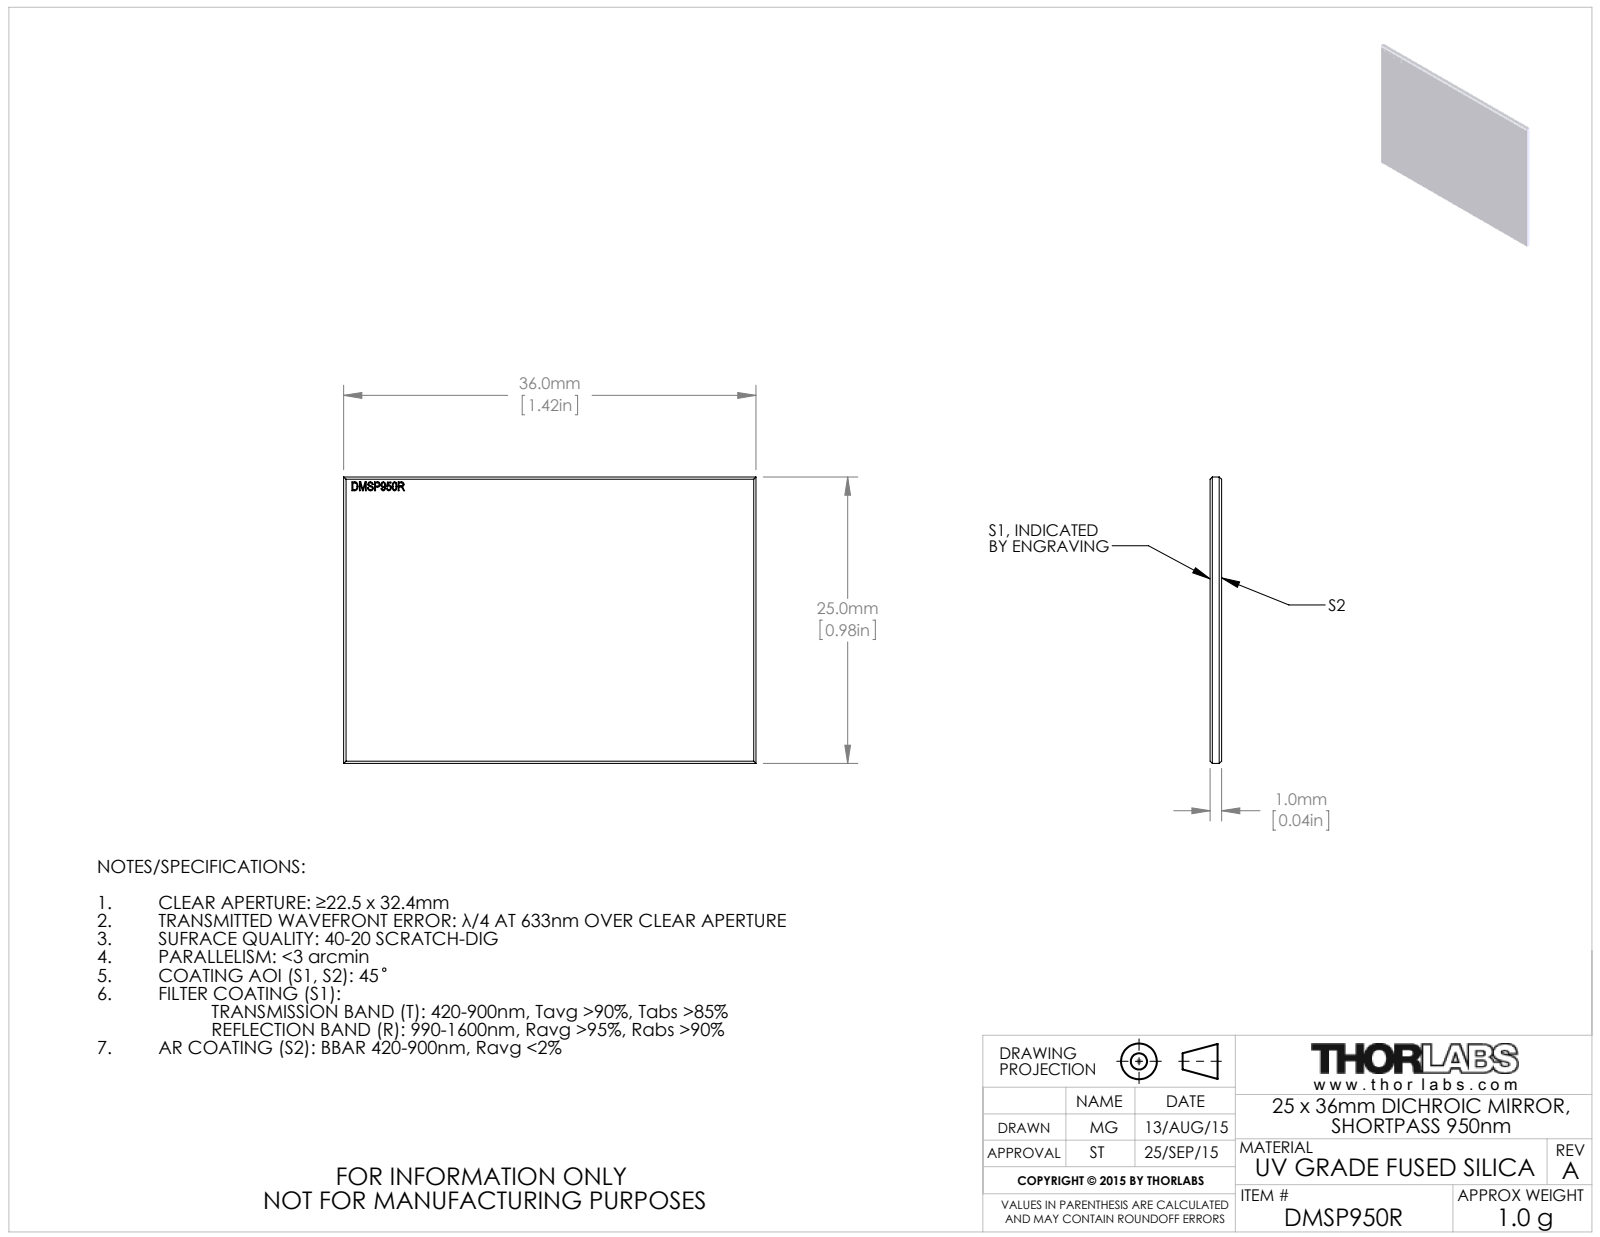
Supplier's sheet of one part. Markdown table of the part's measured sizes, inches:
| quantity | value |
| --- | --- |
| part name | TTN045008-E0W |
| STEP written by | SolidWorks 2014 (CONFIG_CONTROL_DESIGN) |
| units | inches |
| bodies | 1 solid, 140 faces (77 planar, 0 cylindrical, 63 other) |
| overall size | 1.417 × 0.984 × 0.039 |
| volume | 0.055 in³ |
| surface area | 2.936 in² |
| main face-to-face distances | 0.039, 0.984, 0.713, 1.417, 1.019, 0.039, 0.028, 0.078, 0.031, 0.021 |
